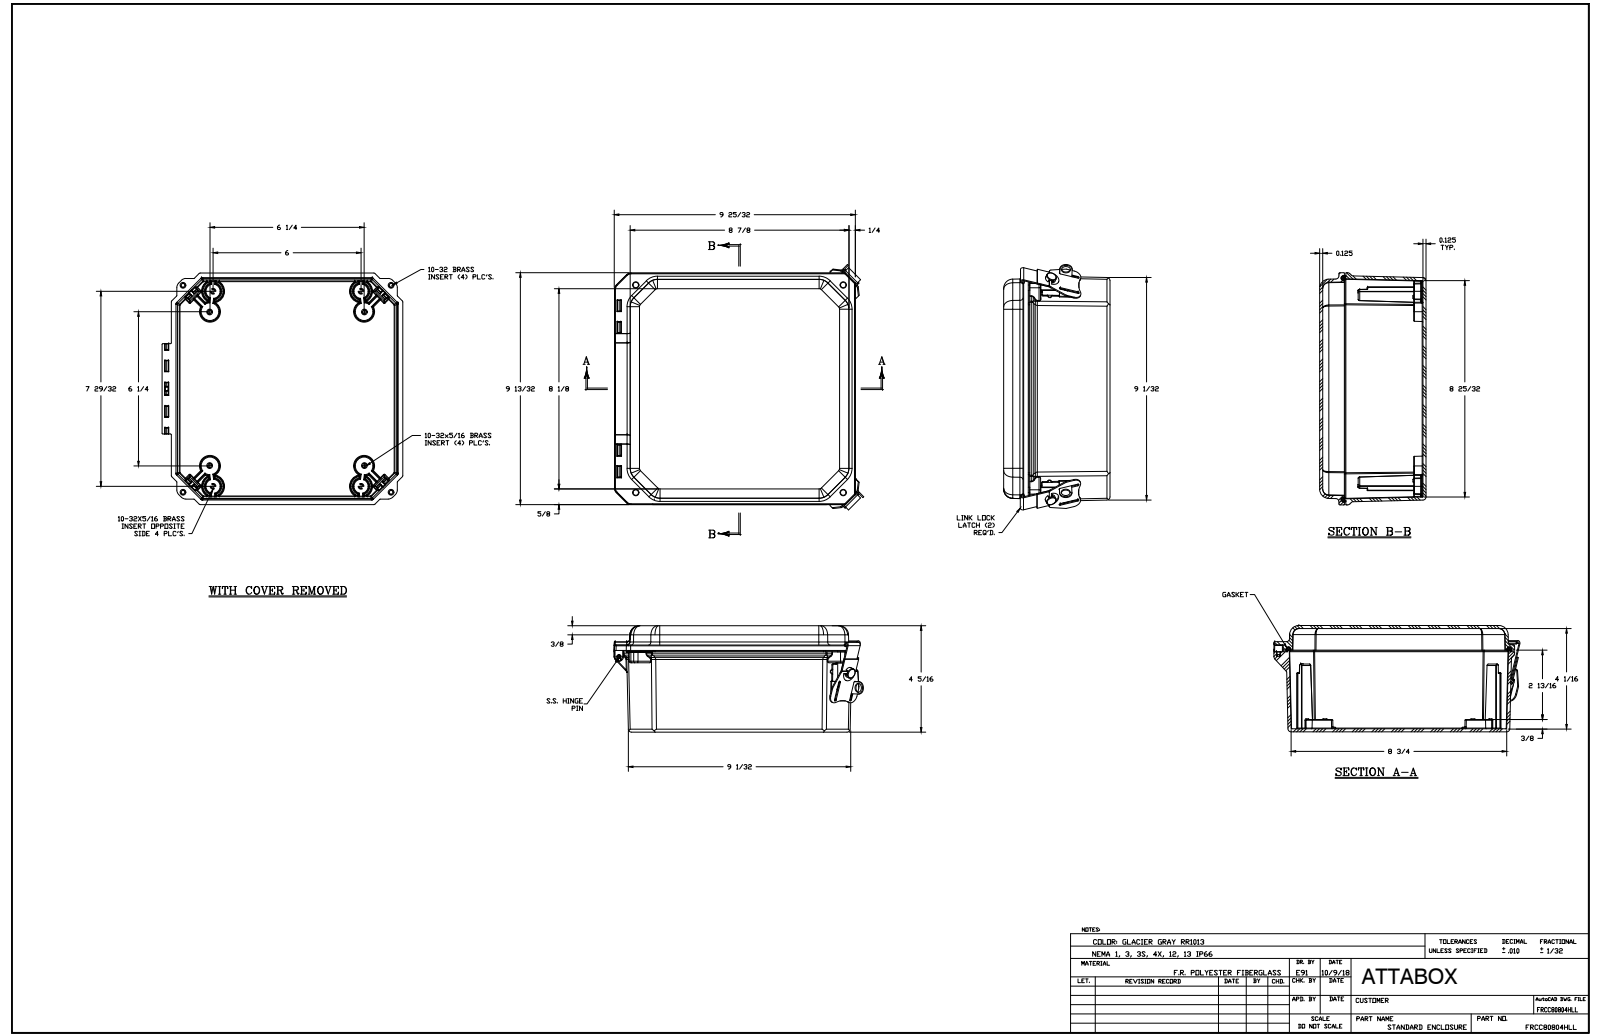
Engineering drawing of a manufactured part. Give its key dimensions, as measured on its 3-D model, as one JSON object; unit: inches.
{"part_name": "FRCC80804HLL", "step_written_by": "SolidWorks 2018 (AUTOMOTIVE_DESIGN)", "units": "inches", "bodies": {"solids": 33, "faces": 2205, "planar": 646, "cylindrical": 853, "other": 706}, "overall_size": [10.263, 10.202, 4.312], "volume_in3": 45.37, "surface_area_in2": 717.5, "round_holes": [[0.156, 12], [0.152, 8], [0.098, 4], [0.15, 4], [0.219, 4], [0.252, 4], [0.312, 4], [0.05, 2], [0.12, 2], [0.363, 2], [0.137, 1]], "round_bosses_or_shafts": [[0.246, 12], [0.87, 4], [0.209, 4], [0.2, 4], [0.6, 2], [0.135, 2], [0.05, 2], [0.135, 1]], "partial_cylinders_radius": [[0.01, 160], [0.005, 94], [0.02, 67], [0.125, 41], [0.03, 38], [0.039, 28], [0.25, 26], [0.03, 24]], "face_to_face_distances": [0.125, 4.187, 4.062, 4.312, 0.124, 3.531, 0.656, 0.875, 3.406, 0.781], "hole_center_spacings": [6.25, 6.25, 7.411, 0.837, 6.181, 7.08, 7.411, 8.414]}
